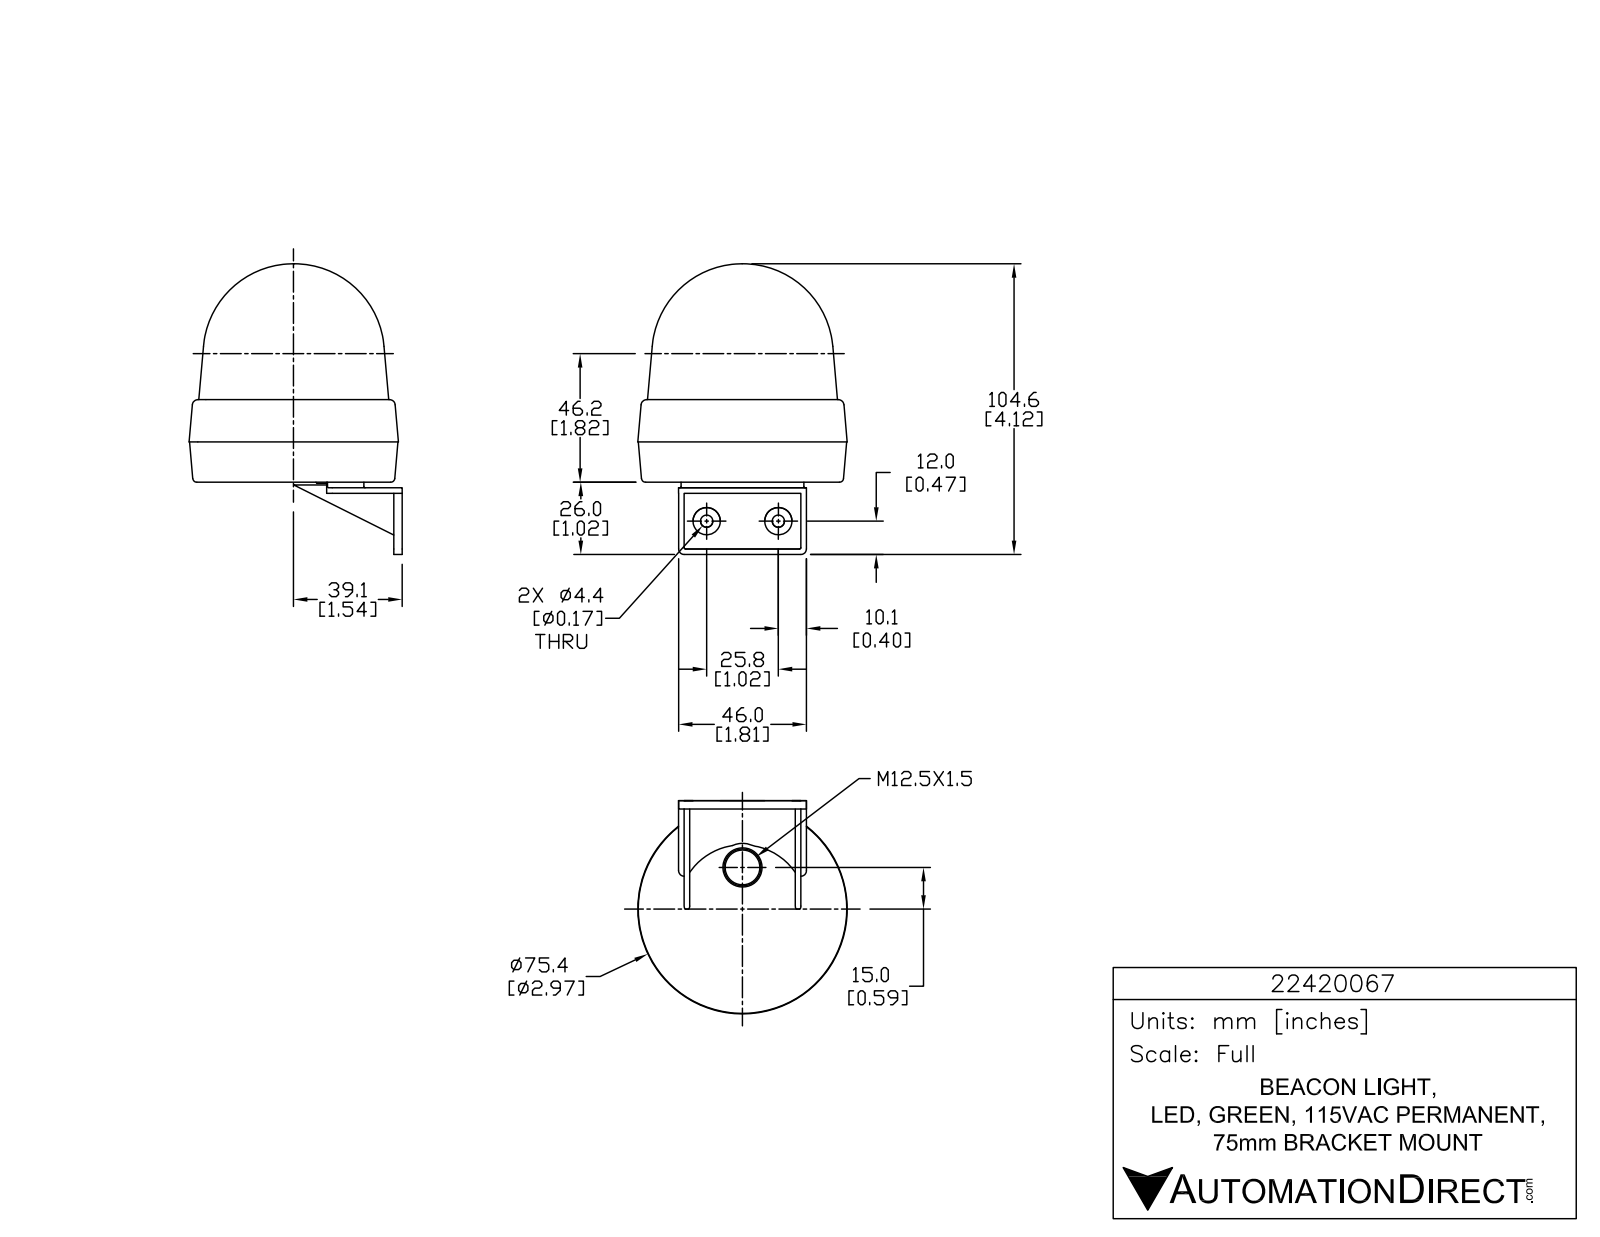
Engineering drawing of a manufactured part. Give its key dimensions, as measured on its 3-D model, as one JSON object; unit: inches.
{"part_name": "22420067", "step_written_by": "SolidWorks 2015 (AUTOMOTIVE_DESIGN)", "units": "inches", "bodies": {"solids": 1, "faces": 819, "planar": 549, "cylindrical": 180, "other": 90}, "overall_size": [4.117, 3.253, 2.967], "volume_in3": 16.02, "surface_area_in2": 41.97, "round_holes": [[0.059, 3], [0.173, 2]], "round_bosses_or_shafts": [[0.339, 3], [0.084, 3], [0.386, 2]], "partial_cylinders_radius": [[0.005, 9], [0.005, 6], [0.012, 6], [0.012, 6], [0.012, 6], [0.02, 6], [0.196, 6], [0.079, 4]], "face_to_face_distances": [0.079, 0.157, 1.574, 0.039, 0.118, 1.653, 1.496, 0.079, 1.654, 1.732], "hole_center_spacings": [1.016]}
